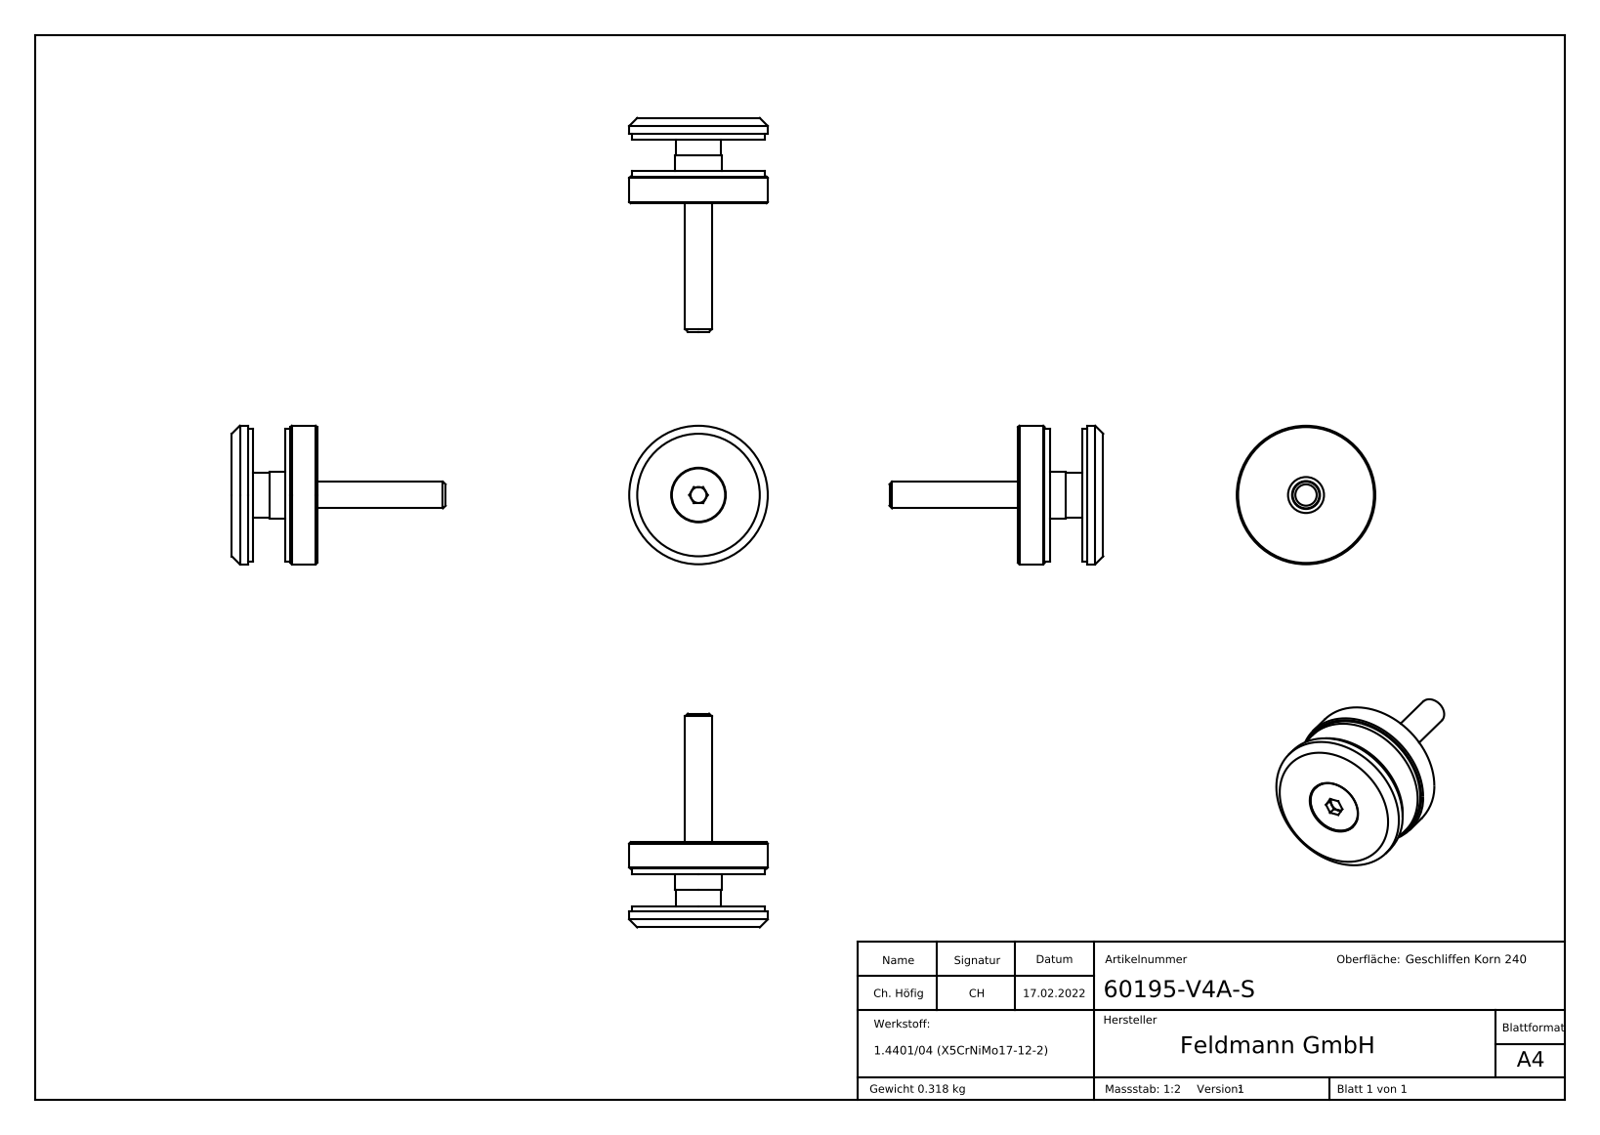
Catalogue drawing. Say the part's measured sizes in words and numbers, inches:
The part is named "60195-V4A-S; 60195-V4A-S Teil5; 60195-V4A-S Teil4; 60195-V4A-S Teil2_60195-V4A-S Teil2 (+8 more)". Its 3-D file was written by "SolidWorks 2018 (CONFIG_CONTROL_DESIGN)". It is 6 solids with 318 faces: 166 planar, 30 cylindrical and 122 other. Overall it measures 3.159 by 2.047 by 2.047 inches. Its volume is 2.877 cubic inches and its surface area 37.35 square inches. Round holes: 1 of diameter 0.413, 1 of diameter 0.551, 1 of diameter 0.807. Round bosses or shafts: 1 of diameter 2.047, 1 of diameter 1.969, 1 of diameter 0.787, 1 of diameter 0.689, 1 of diameter 0.669, 1 of diameter 0.394. The main face-to-face distances are 0.551, 0.079, 0.63, 0.472, 0.236, 0.394, 1.024, 0.315, 0.945, 1.26.
